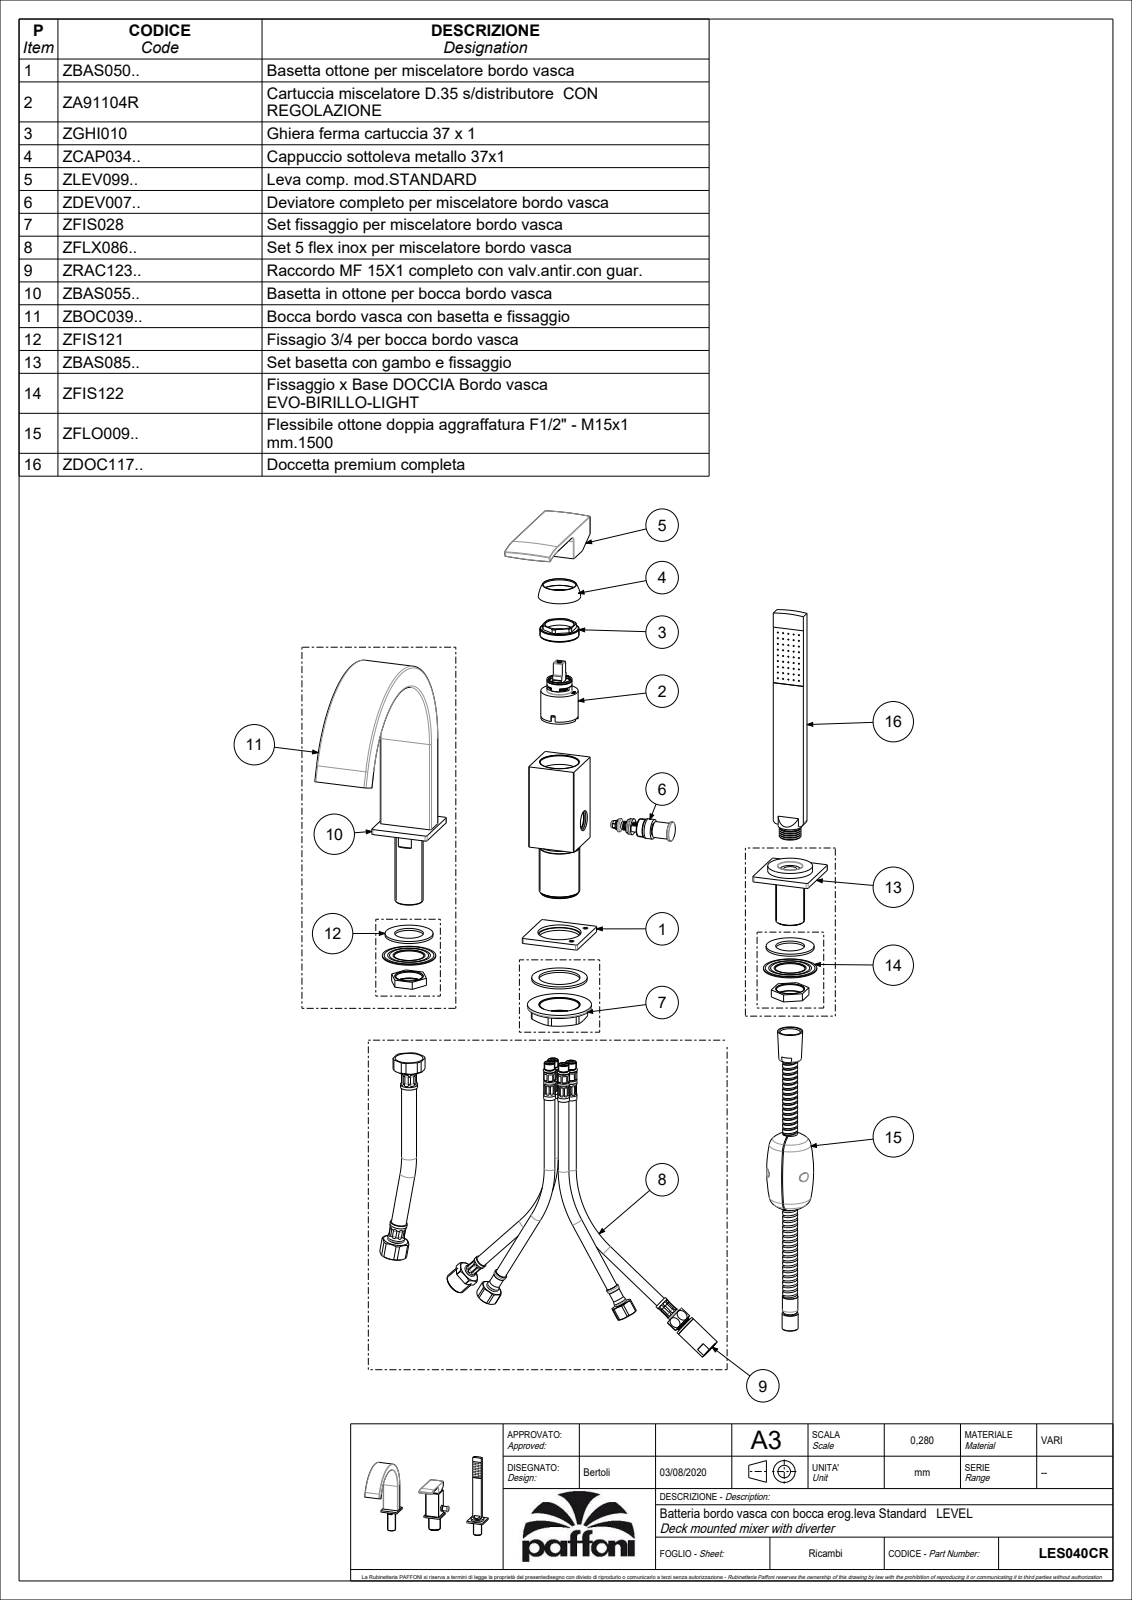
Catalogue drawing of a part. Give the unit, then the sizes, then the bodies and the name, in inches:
Units: inches
Overall size (bounding box): 13.976 × 8.78 × 8.542
Round holes (diameter × count): ⌀0.276 ×7, ⌀1.89 ×3, ⌀0.157 ×2, ⌀0.122 ×1, ⌀0.13 ×1, ⌀0.134 ×1, ⌀0.169 ×1, ⌀0.177 ×1, ⌀0.197 ×1, ⌀0.217 ×1, ⌀0.283 ×1, ⌀0.354 ×1
Round bosses / shafts (diameter × count): ⌀0.079 ×11, ⌀1.673 ×3, ⌀0.591 ×2, ⌀1.654 ×1, ⌀1.575 ×1, ⌀1.496 ×1, ⌀1.378 ×1, ⌀1.37 ×1
Partial cylindrical surfaces — rounded edges, fillets, slot ends (radius × count): R0.059 ×38, R0.02 ×33, R0.006 ×11, R0.012 ×4, R0.079 ×4, R0.039 ×2, R0.157 ×2, R11.811 ×2
Main face-to-face distances: 0.138, 0.197, 0.689, 1.28, 0.492, 0.591, 1.772, 1.87, 1.083, 0.059
Hole centre spacings: 0.118, 0.339, 0.419, 0.551, 0.564, 5.633, 5.639, 5.906
Volume: 27.42 in³ · Surface area: 313.9 in²
Bodies: 7 solids, 1559 faces (938 planar, 391 cylindrical, 230 other)
Part name (STEP PRODUCT): LES040CR
STEP written by: CREO PARAMETRIC BY PTC INC, 2020044 (CONFIG_CONTROL_DESIGN)
